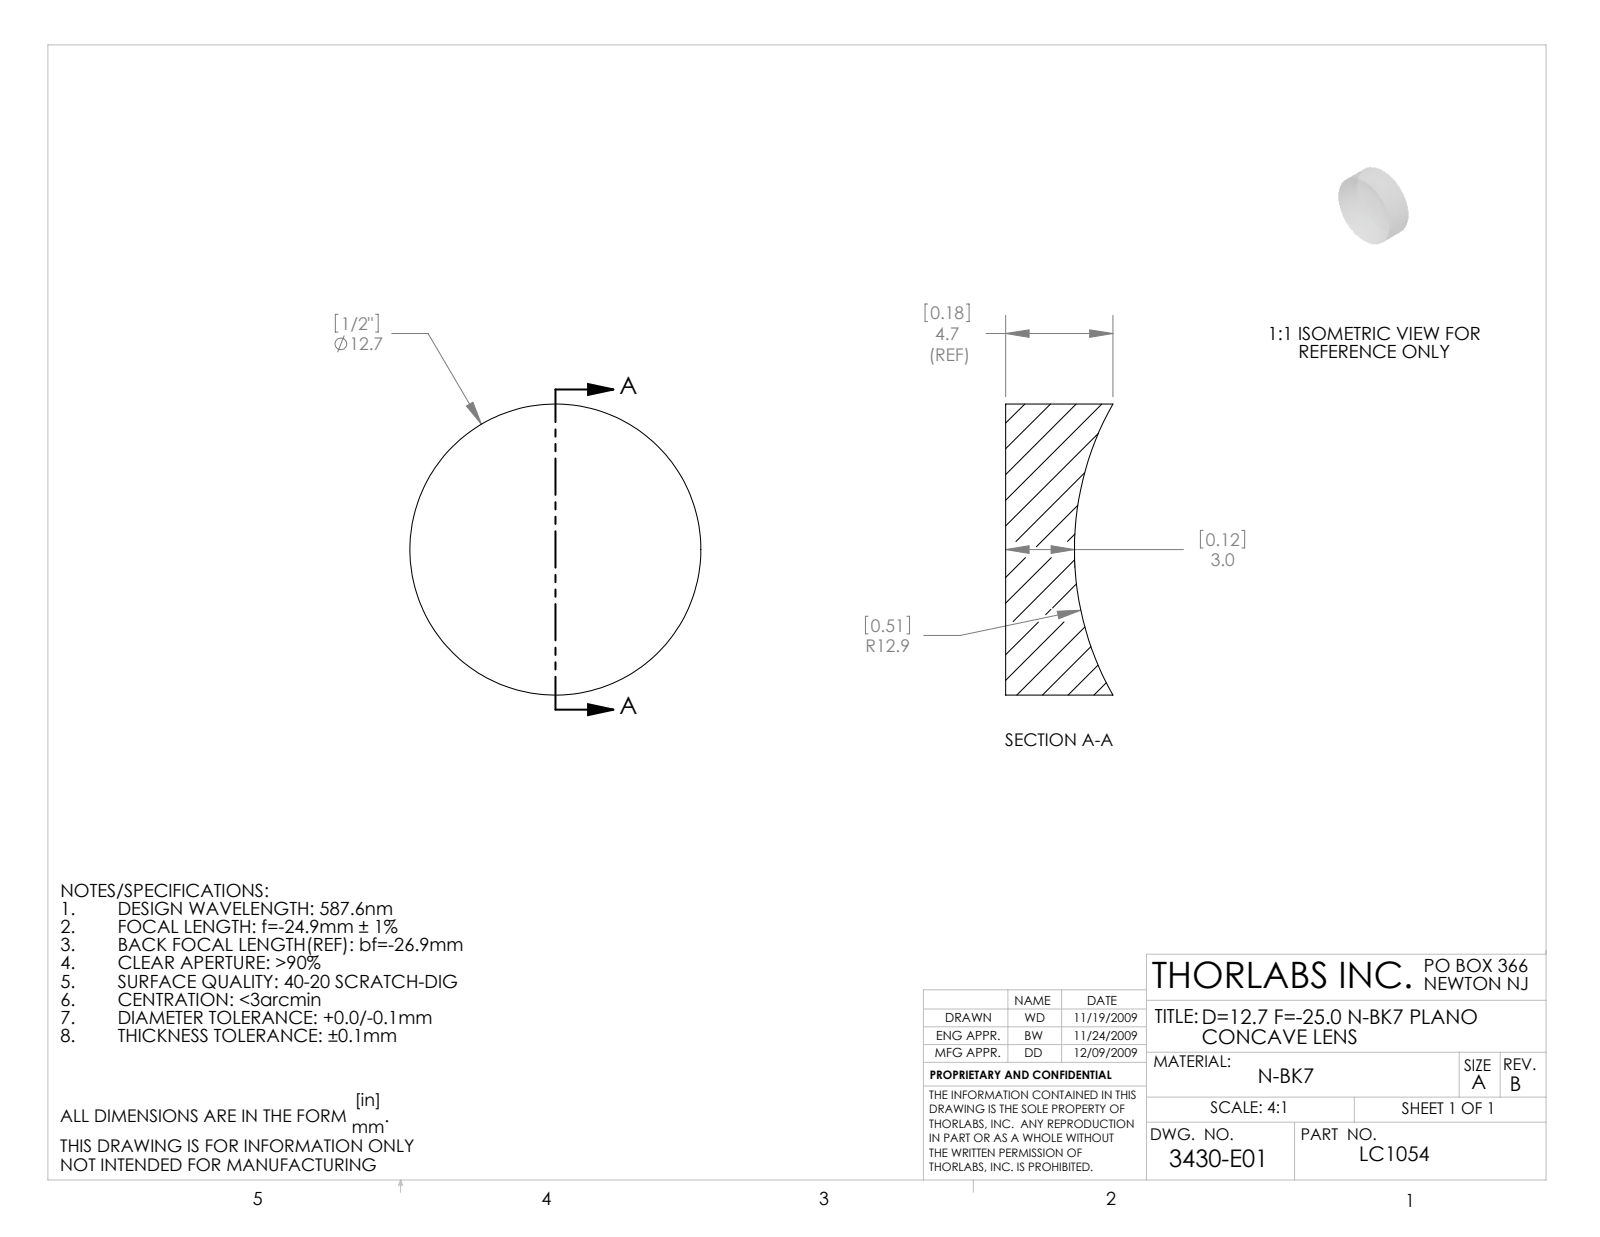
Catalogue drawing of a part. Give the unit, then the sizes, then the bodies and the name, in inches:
Units: inches
Overall size (bounding box): 0.5 × 0.5 × 0.184
Round bosses / shafts (diameter × count): ⌀0.5 ×1
Volume: 0.03 in³ · Surface area: 0.696 in²
Bodies: 1 solid, 5 faces (1 planar, 2 cylindrical, 2 other)
Part name (STEP PRODUCT): 3430-E0W
STEP written by: SolidWorks 2009 (AUTOMOTIVE_DESIGN)
